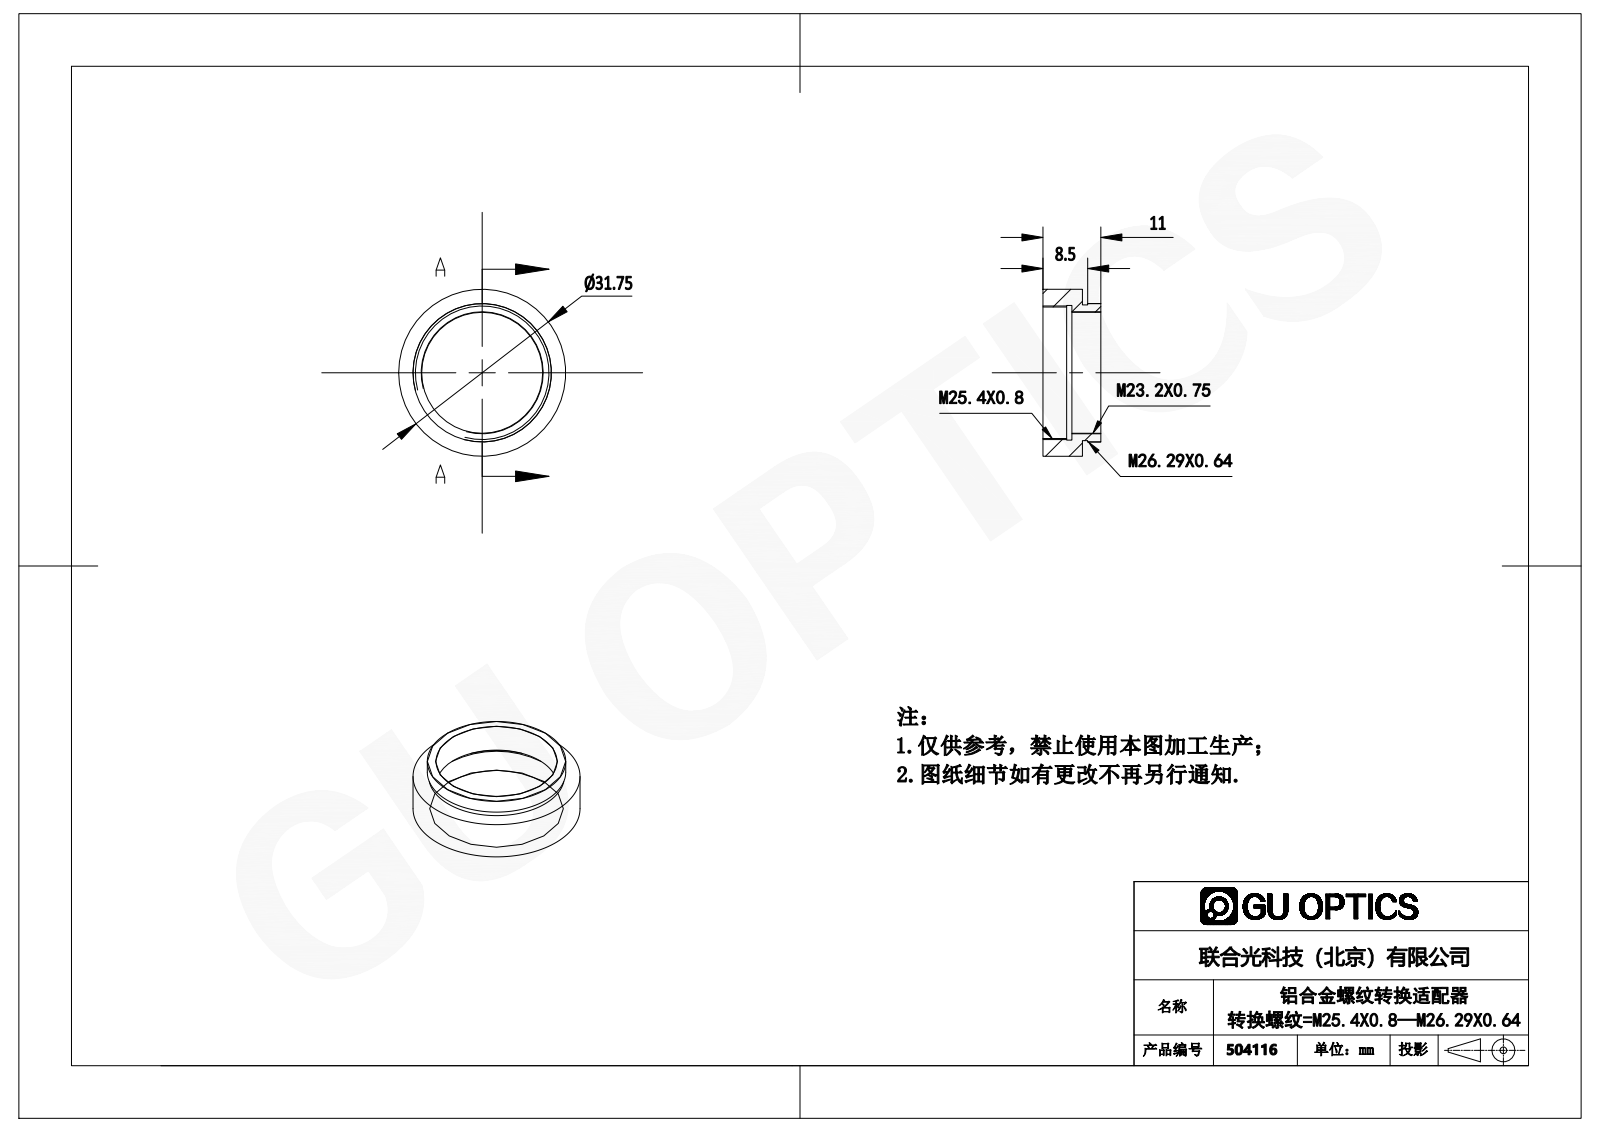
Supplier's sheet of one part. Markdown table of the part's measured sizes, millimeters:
| quantity | value |
| --- | --- |
| part name | 504116 |
| STEP written by | SolidWorks 2016 (AUTOMOTIVE_DESIGN) |
| units | millimeters |
| bodies | 1 solid, 18 faces (6 planar, 12 cylindrical, 0 other) |
| overall size | 31.75 × 31.75 × 11 |
| volume | 2 812 mm³ |
| surface area | 2 710 mm² |
| round holes (diameter × count) | 23 × 1, 25 × 1, 25.6 × 1 |
| round bosses / shafts (diameter × count) | 31.75 × 1, 26.32 × 1, 25.8 × 1 |
| main face-to-face distances | 7.5, 5.5, 11, 3.5, 2, 1, 3, 4.5, 6.5, 8.5 |
